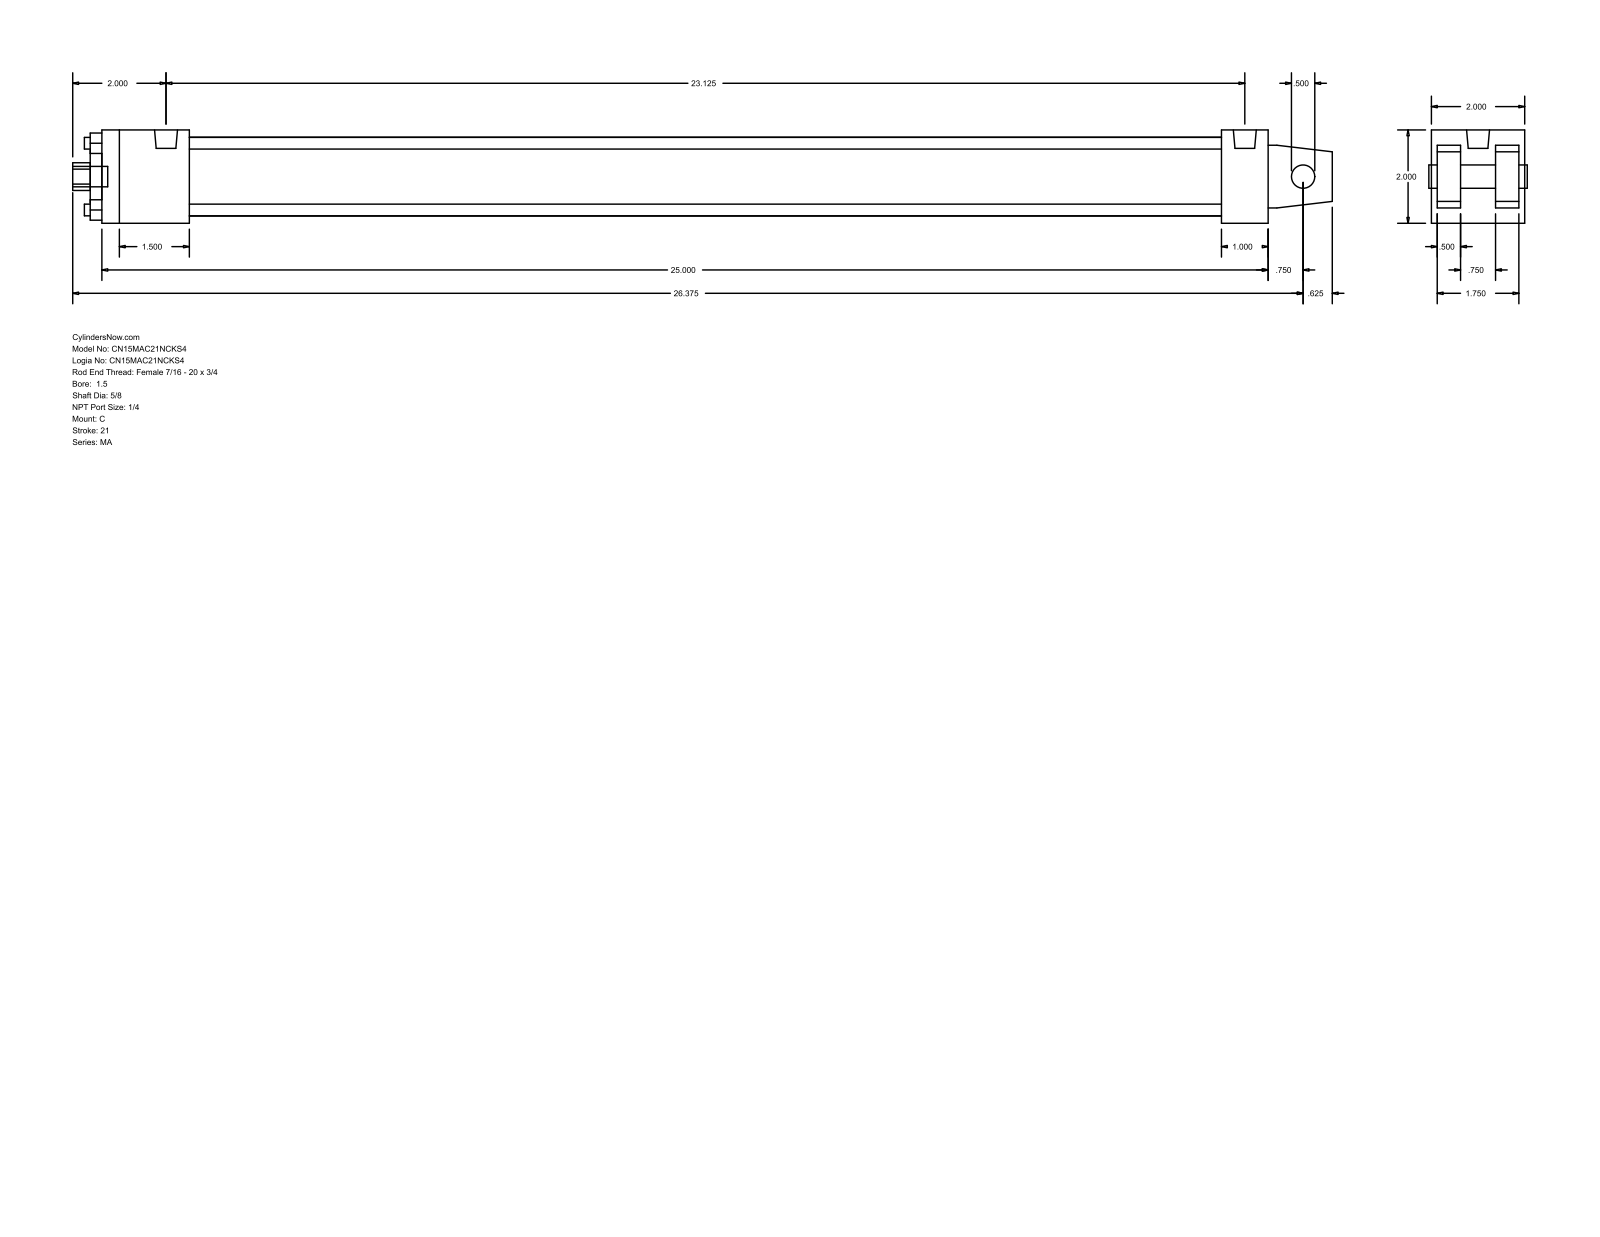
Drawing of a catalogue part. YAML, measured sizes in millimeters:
part_name: "MA_C__0150_0.625"
step_written_by: "GSSL Pune (CONFIG_CONTROL_DESIGN)"
units: millimeters
bodies: {solids: 0, faces: 103, planar: 76, cylindrical: 27, other: 0}
overall_size: [685.8, 50.8, 50.8]
round_holes:
  - {diameter: 6.35, count: 4}
  - {diameter: 12.7, count: 1}
  - {diameter: 15.88, count: 1}
  - {diameter: 28.57, count: 1}
  - {diameter: 42.93, count: 1}
round_bosses_or_shafts:
  - {diameter: 7.94, count: 4}
  - {diameter: 12.49, count: 2}
  - {diameter: 11.11, count: 1}
partial_cylinders:
  - {radius: 7.54, count: 1}
face_to_face_distances: [50.8, 12.7, 3.17, 15.87, 34.93, 47.63, 31.76, 635, 609.6, 25.4]
hole_center_spacings: [25.68, 36.32, 51.36]
